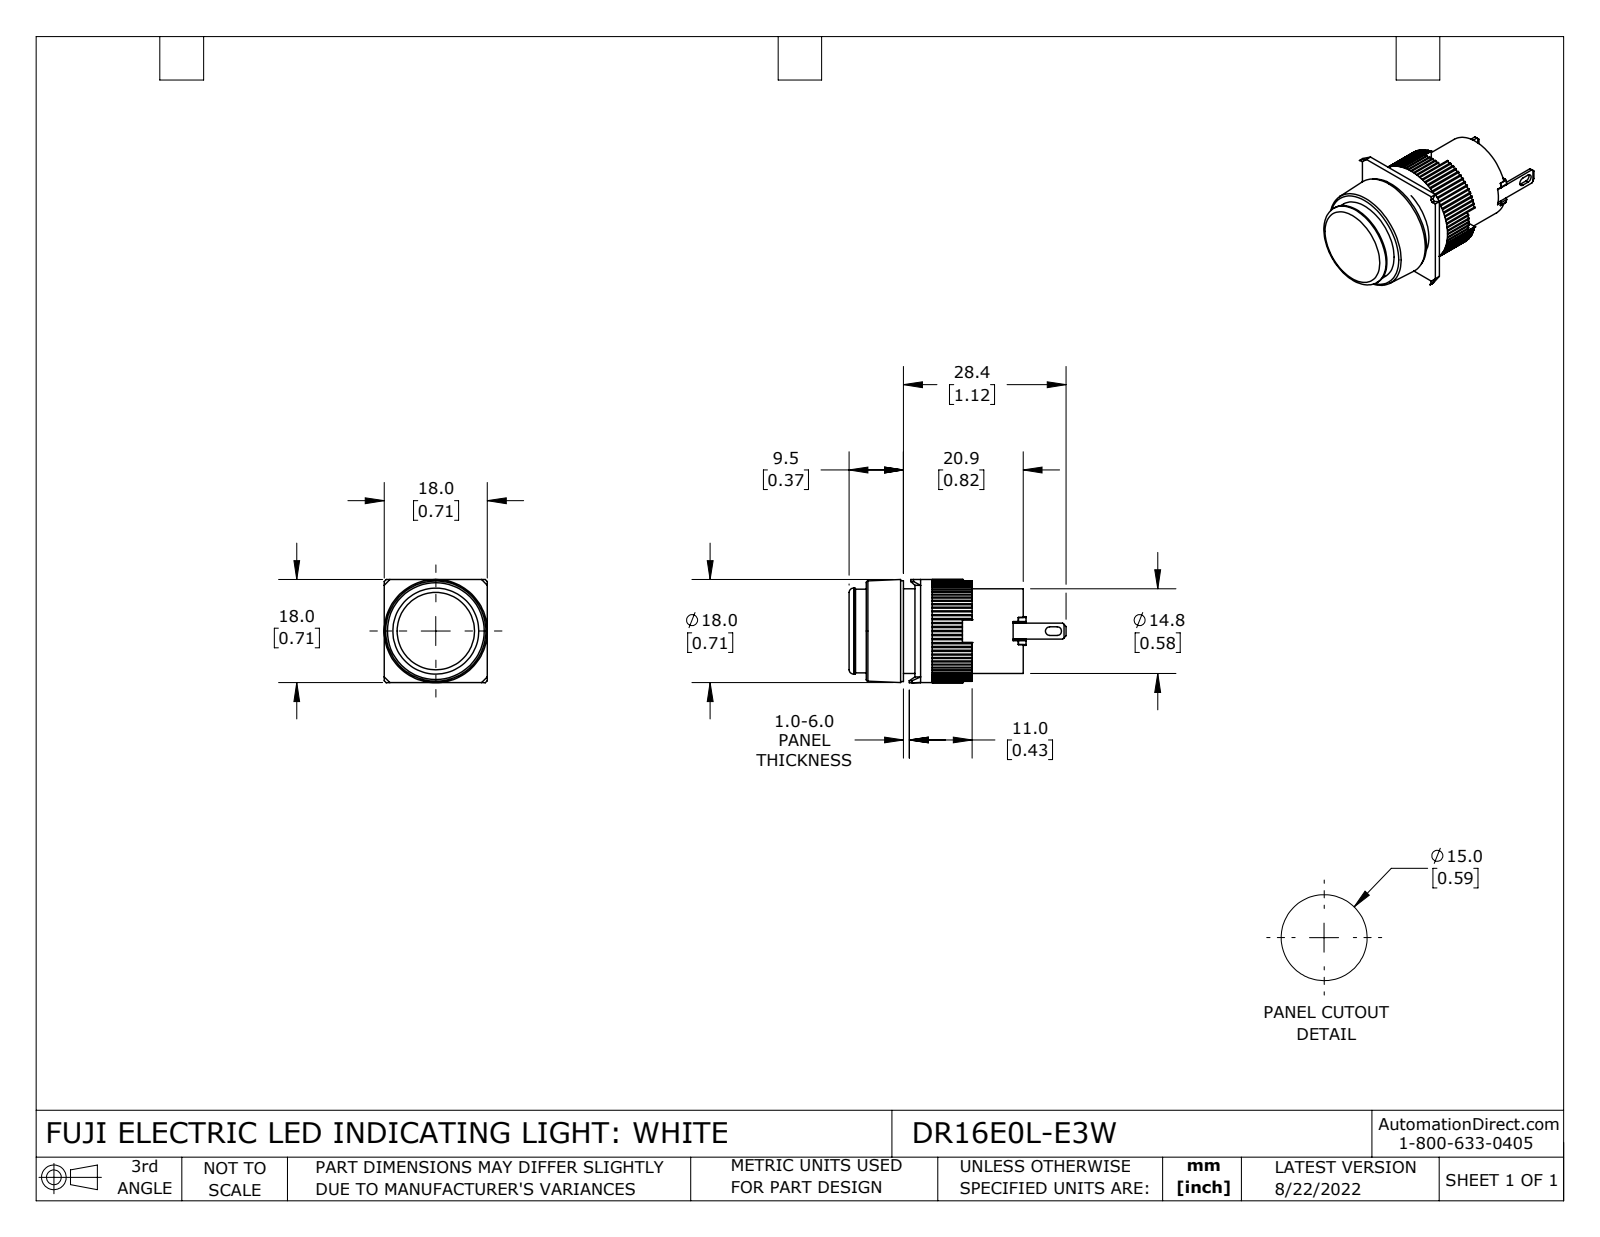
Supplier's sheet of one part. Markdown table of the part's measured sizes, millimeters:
| quantity | value |
| --- | --- |
| part name | DR16E0L-E3W |
| STEP written by | SolidWorks 2021 (CONFIG_CONTROL_DESIGN) |
| units | millimeters |
| bodies | 10 solids, 476 faces (295 planar, 171 cylindrical, 10 other) |
| overall size | 37.9 × 18 × 18 |
| volume | 5 720 mm³ |
| surface area | 4 661 mm² |
| round holes (diameter × count) | 13.8 × 1, 14.6 × 1, 14.8 × 1 |
| round bosses / shafts (diameter × count) | 18 × 1, 17.6 × 1, 15 × 1 |
| partial cylindrical surfaces (radius × count) | 0.3 × 80, 0.2 × 8, 0.8 × 2 |
| main face-to-face distances | 3.5, 8.9, 17.9, 9, 12.5, 5.4, 11.5, 21.4, 2.5, 1 |
